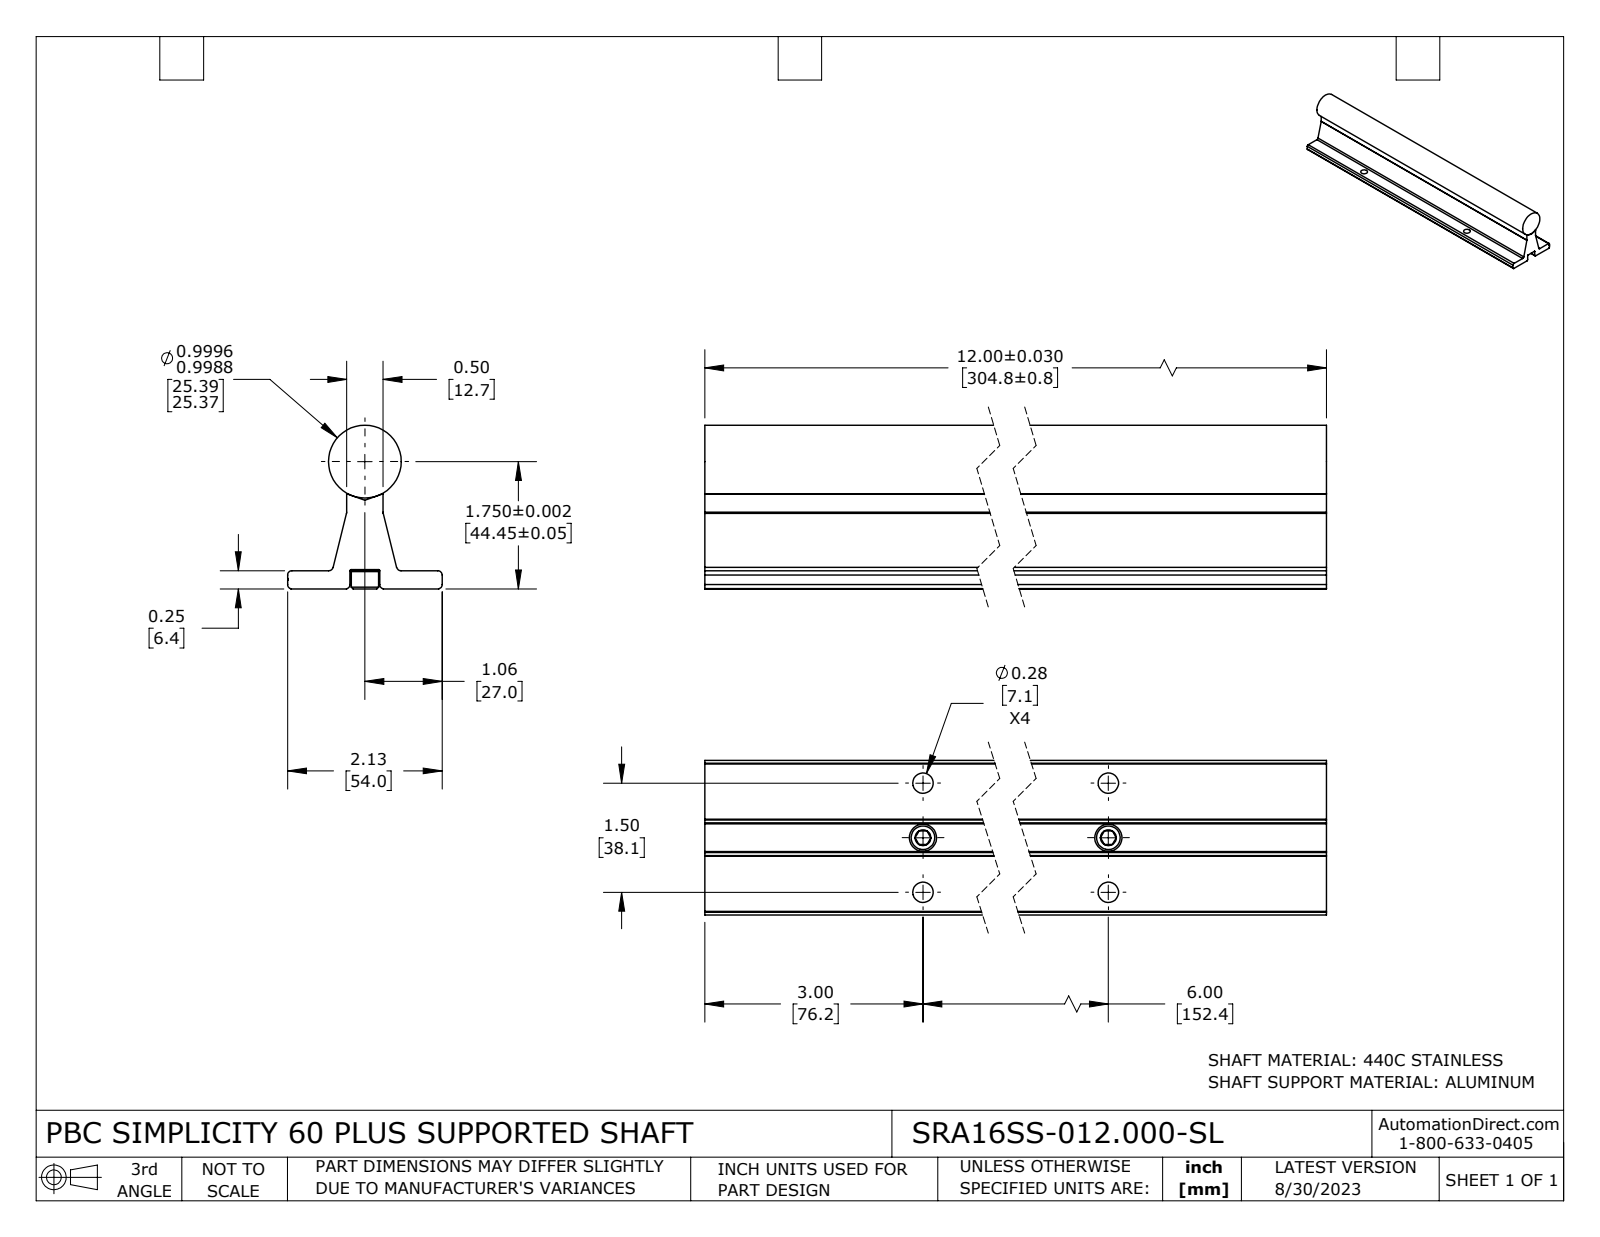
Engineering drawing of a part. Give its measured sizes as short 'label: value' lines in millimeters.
name: SRA16SS-012.000-SL
written by: SolidWorks 2021 (CONFIG_CONTROL_DESIGN)
unit: mm
bodies: 4 solids, 123 faces (49 planar, 44 cylindrical, 30 other)
size: 304.8 × 57.2 × 54
volume: 366 700 mm³; area: 84 260 mm²
holes: 6× ⌀7.1, 2× ⌀5.4, 2× ⌀8
bosses: 2× ⌀9.5, 2× ⌀6.4, 1× ⌀25.4
rounds: 6× R1.5, 4× R1.6, 2× R0.4, 2× R0.8
face distances: 6.4, 1.1, 11.6, 6.7, 0.4, 12.7, 20.7, 21.8, 32.2, 33.4
hole spacings: 19.1, 153.6, 152.4, 38.1, 157.1
